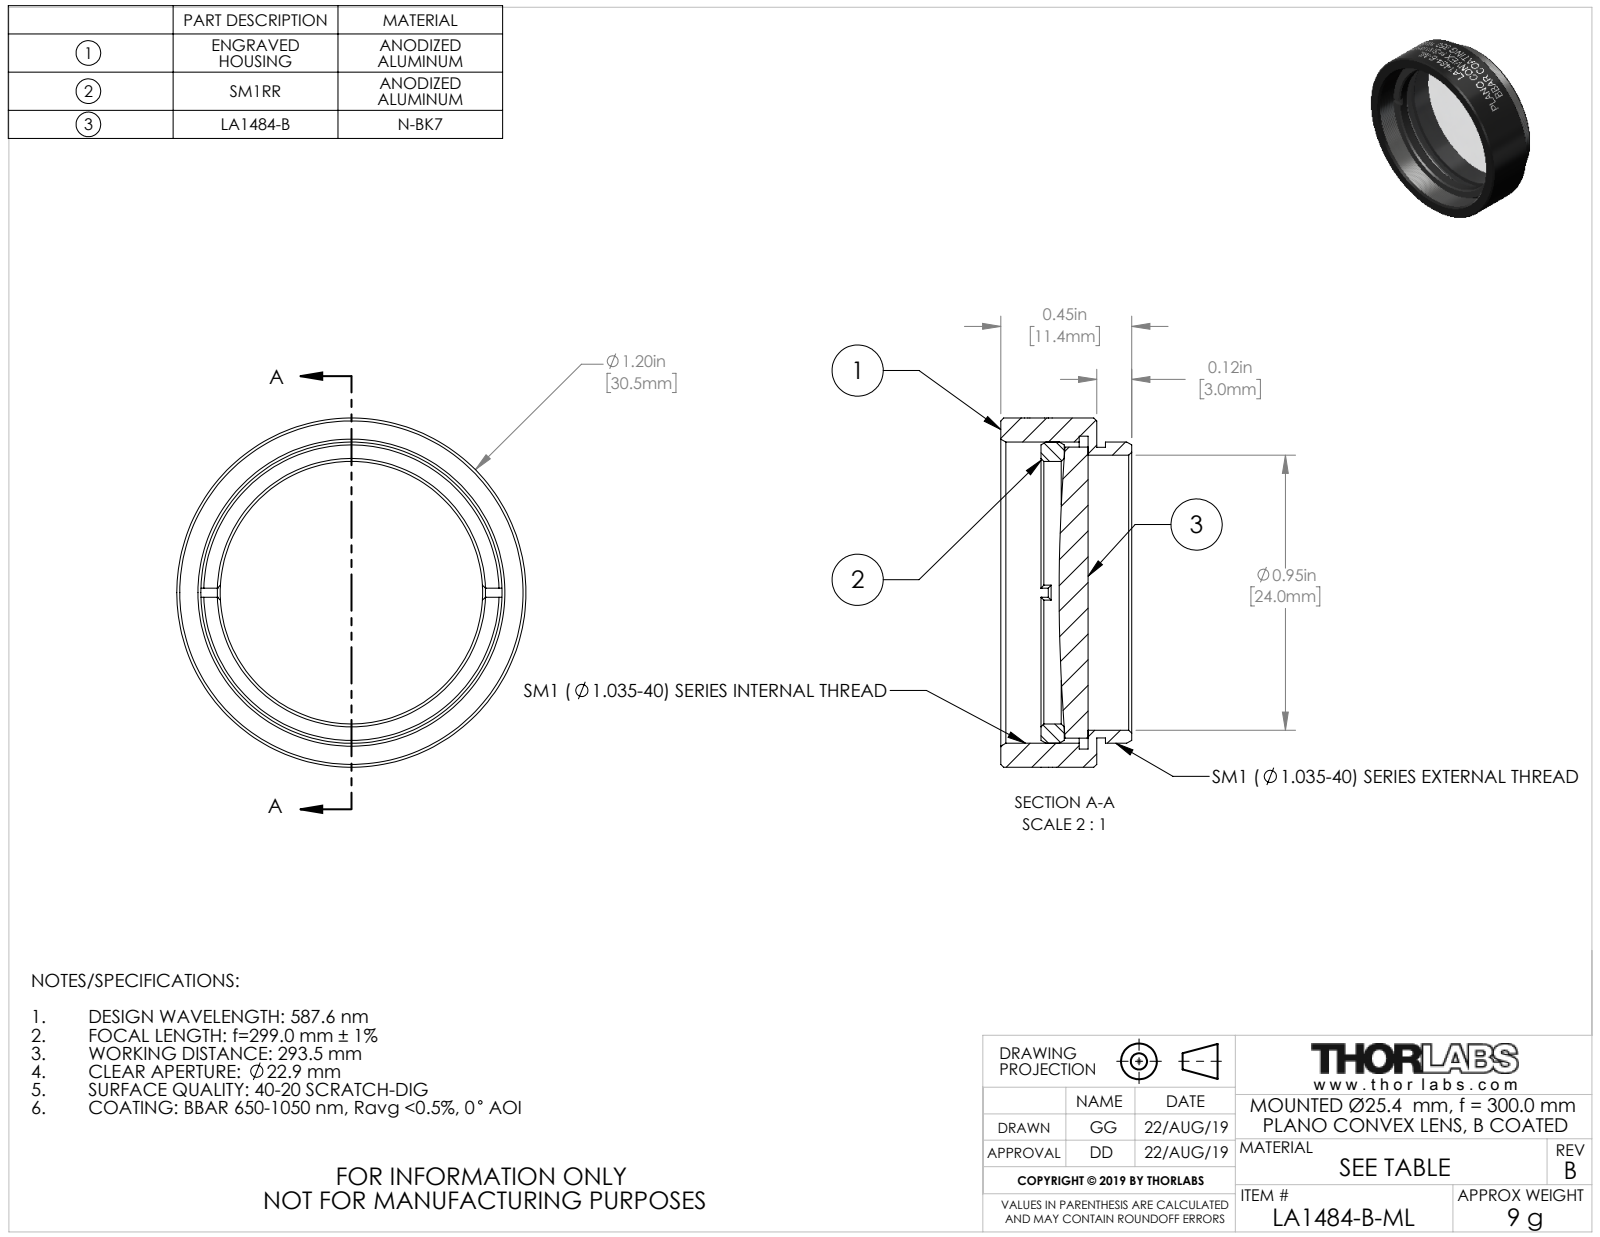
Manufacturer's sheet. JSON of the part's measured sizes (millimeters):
{"part_name": "24424-E0W", "step_written_by": "SolidWorks 2018 (CONFIG_CONTROL_DESIGN)", "units": "millimeters", "bodies": {"solids": 3, "faces": 158, "planar": 20, "cylindrical": 114, "other": 24}, "overall_size": [30.48, 30.48, 11.43], "volume_mm3": 3226, "surface_area_mm2": 4313, "round_holes": [[22.91, 1], [24, 1], [26.29, 1], [27.3, 1]], "round_bosses_or_shafts": [[30.48, 1], [26.29, 1], [25.4, 1], [25.37, 1]], "face_to_face_distances": [0.76, 8.38, 7.62, 2.84, 2.08, 5.54, 4.87, 4.11, 2.03, 3.51]}
